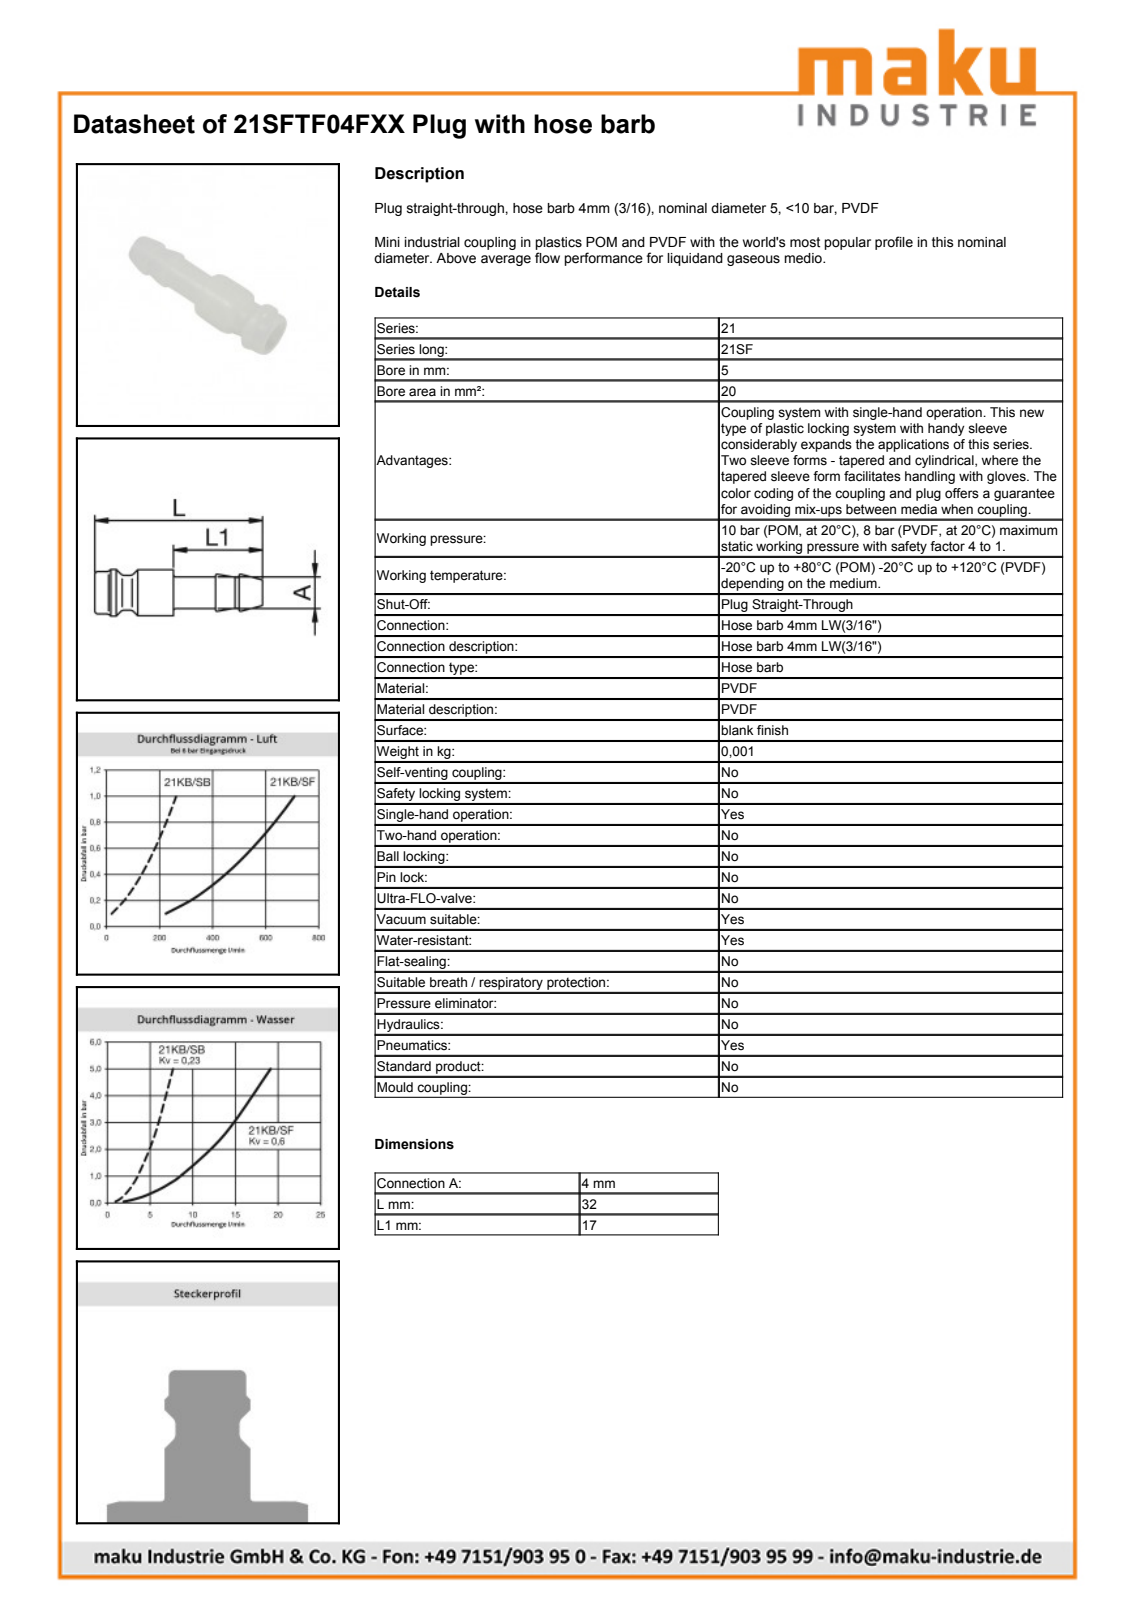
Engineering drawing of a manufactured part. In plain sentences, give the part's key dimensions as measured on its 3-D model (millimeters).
The part is named "D106847". Its 3-D file was written by "Autodesk Inventor 2013 (AUTOMOTIVE_DESIGN)". It is 1 solid with 25 faces: 4 planar, 7 cylindrical and 14 other. Overall it measures 32 by 9 by 9 millimeters. Its volume is 708 cubic millimeters and its surface area 1 090 square millimeters. Round holes: 1 of diameter 2.5, 1 of diameter 4.95. Round bosses or shafts: 1 of diameter 9, 1 of diameter 8.1, 1 of diameter 6.65, 1 of diameter 4.05. The main face-to-face distances are 15, 12.5, 27.5, 4.5, 8, 23.
